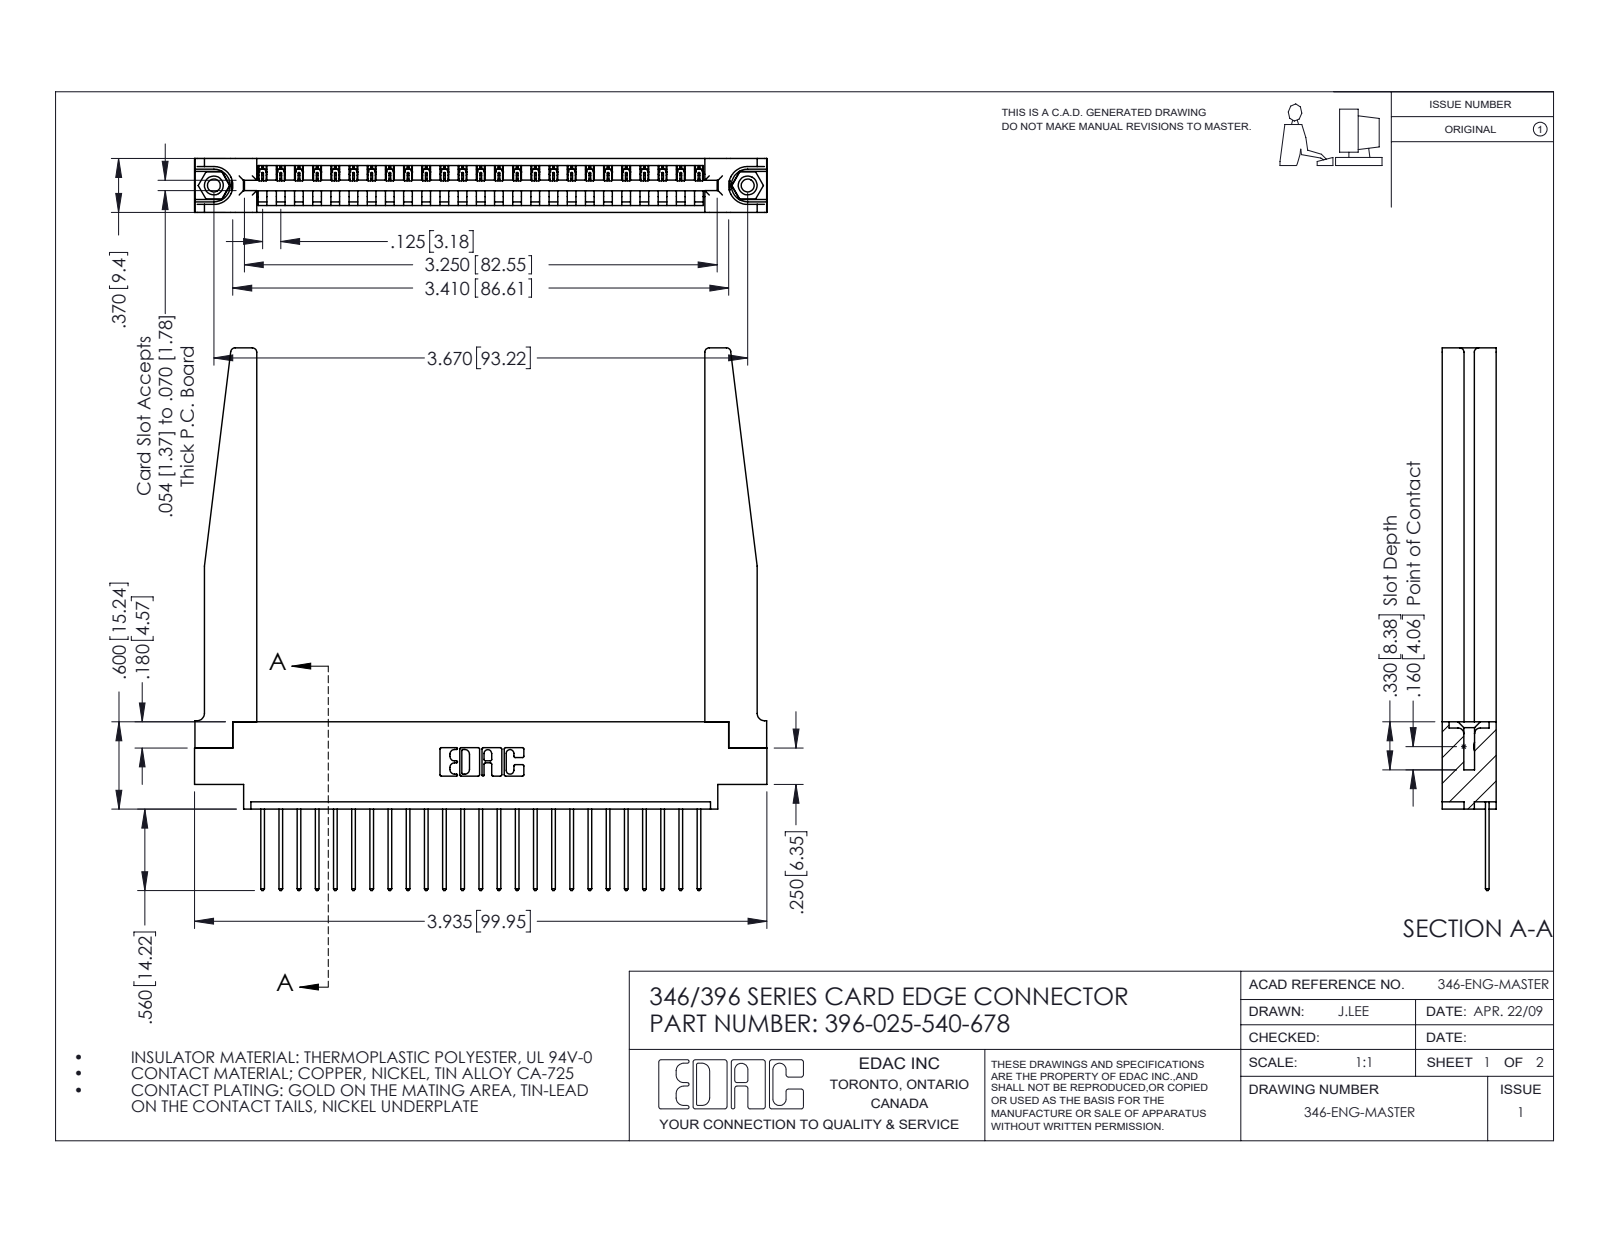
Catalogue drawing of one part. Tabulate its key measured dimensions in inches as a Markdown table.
| quantity | value |
| --- | --- |
| part name | 346 Part_0.170 Offset - 0.156 Dia-TH; 396-025-540-678; 346-220-078_345-220-078; 345-292-001_345-293-140 (+1 more) |
| STEP written by | SolidWorks 2016 (CONFIG_CONTROL_DESIGN) |
| units | inches |
| bodies | 30 solids, 1810 faces (1222 planar, 536 cylindrical, 52 other) |
| overall size | 3.935 × 3.73 × 0.37 |
| volume | 0.991 in³ |
| surface area | 28.56 in² |
| round holes (diameter × count) | 0.089 × 2, 0.125 × 2, 0.156 × 2, 0.064 × 1 |
| round bosses / shafts (diameter × count) | 0.155 × 2 |
| partial cylindrical surfaces (radius × count) | 0.006 × 50, 0.01 × 50, 0.01 × 22, 0.03 × 8, 0.007 × 6, 0.031 × 6, 0.026 × 3, 0.031 × 2 |
| main face-to-face distances | 0.37, 0.048, 0.322, 0.072, 0.148, 0.15, 0.25, 0.298, 0.025, 0.222 |
| hole center spacings | 0.246, 3.462, 3.67 |
